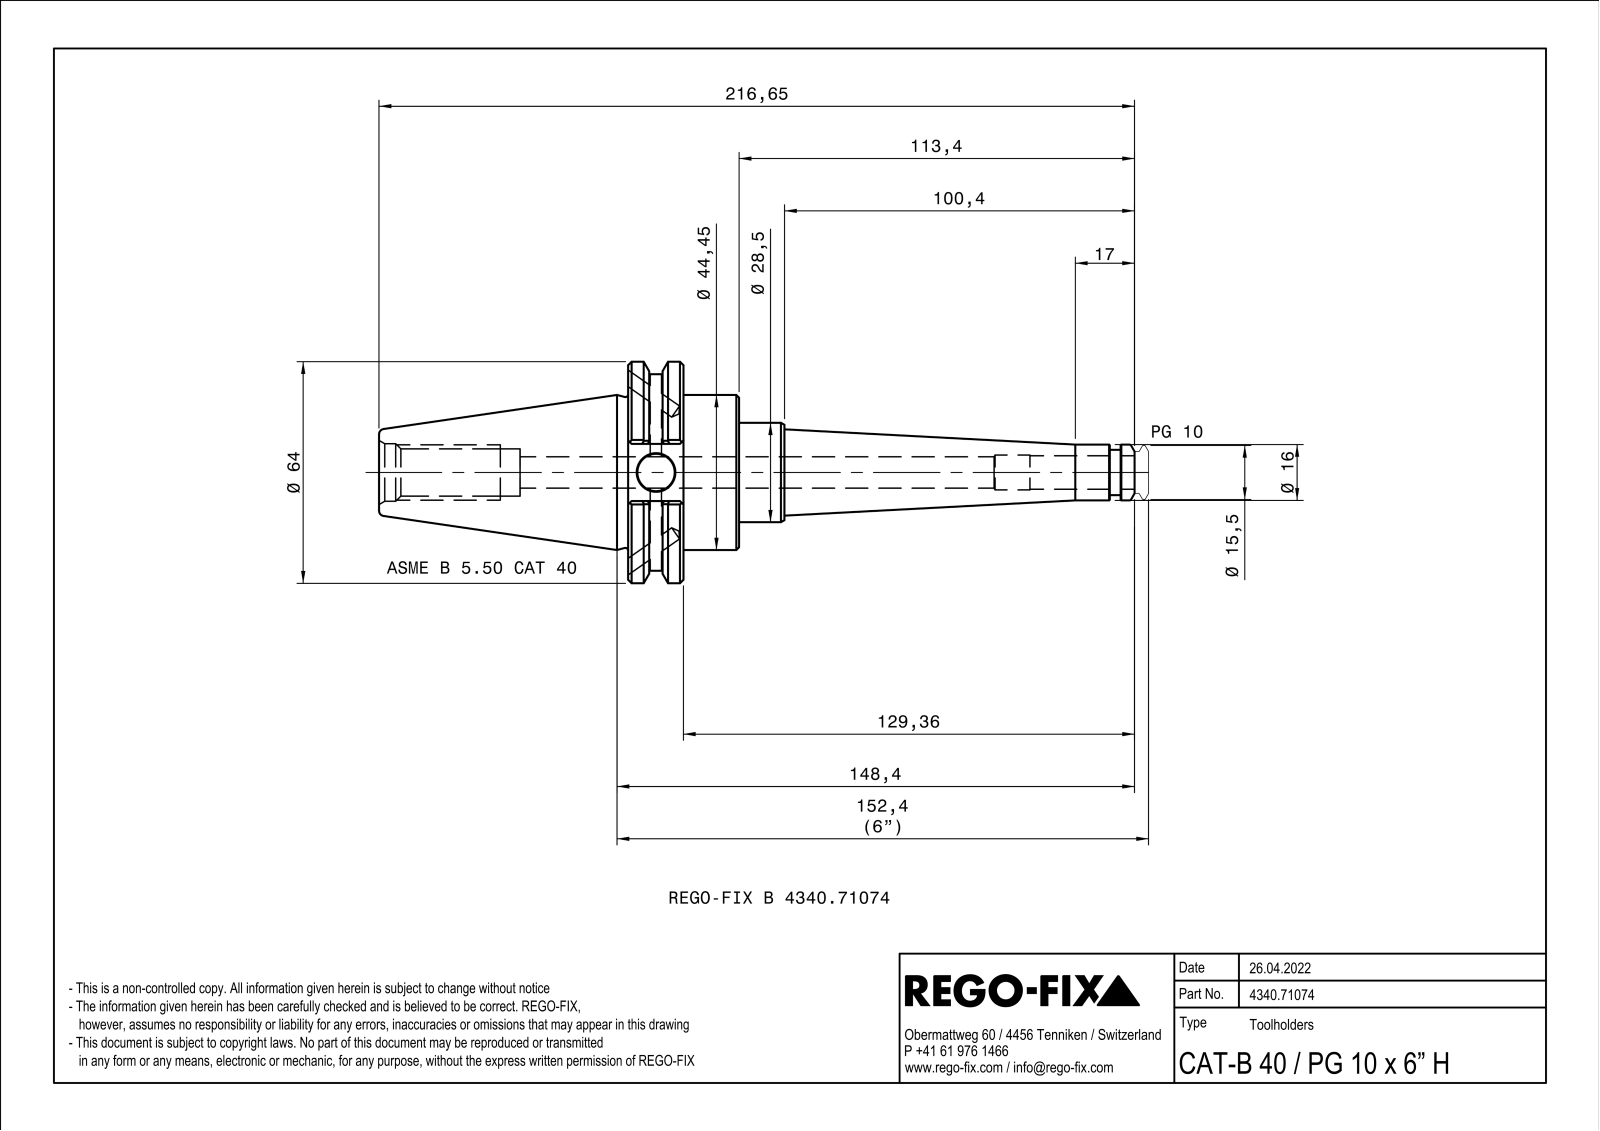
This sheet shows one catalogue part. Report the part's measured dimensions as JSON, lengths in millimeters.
{"part_name": "NOCUT", "step_written_by": "SIEMENS PLM Software Solid Edge ST10 (AUTOMOTIVE_DESIGN)", "units": "millimeters", "bodies": {"solids": 1, "faces": 111, "planar": 35, "cylindrical": 23, "other": 53}, "overall_size": [216.65, 63.5, 60.79], "volume_mm3": 151227, "surface_area_mm2": 33911, "round_holes": [[9, 1], [10, 1], [10.7, 1], [13.53, 1], [16.5, 1]], "round_bosses_or_shafts": [[63.5, 1], [56.36, 1], [44.45, 1], [28.5, 1], [16, 1], [13, 1]], "partial_cylinders_radius": [[0.5, 4]], "face_to_face_distances": [15.87, 15.96, 31.83, 47.33, 16.38, 103.25, 87.29, 71.42, 21.95, 5.99]}
